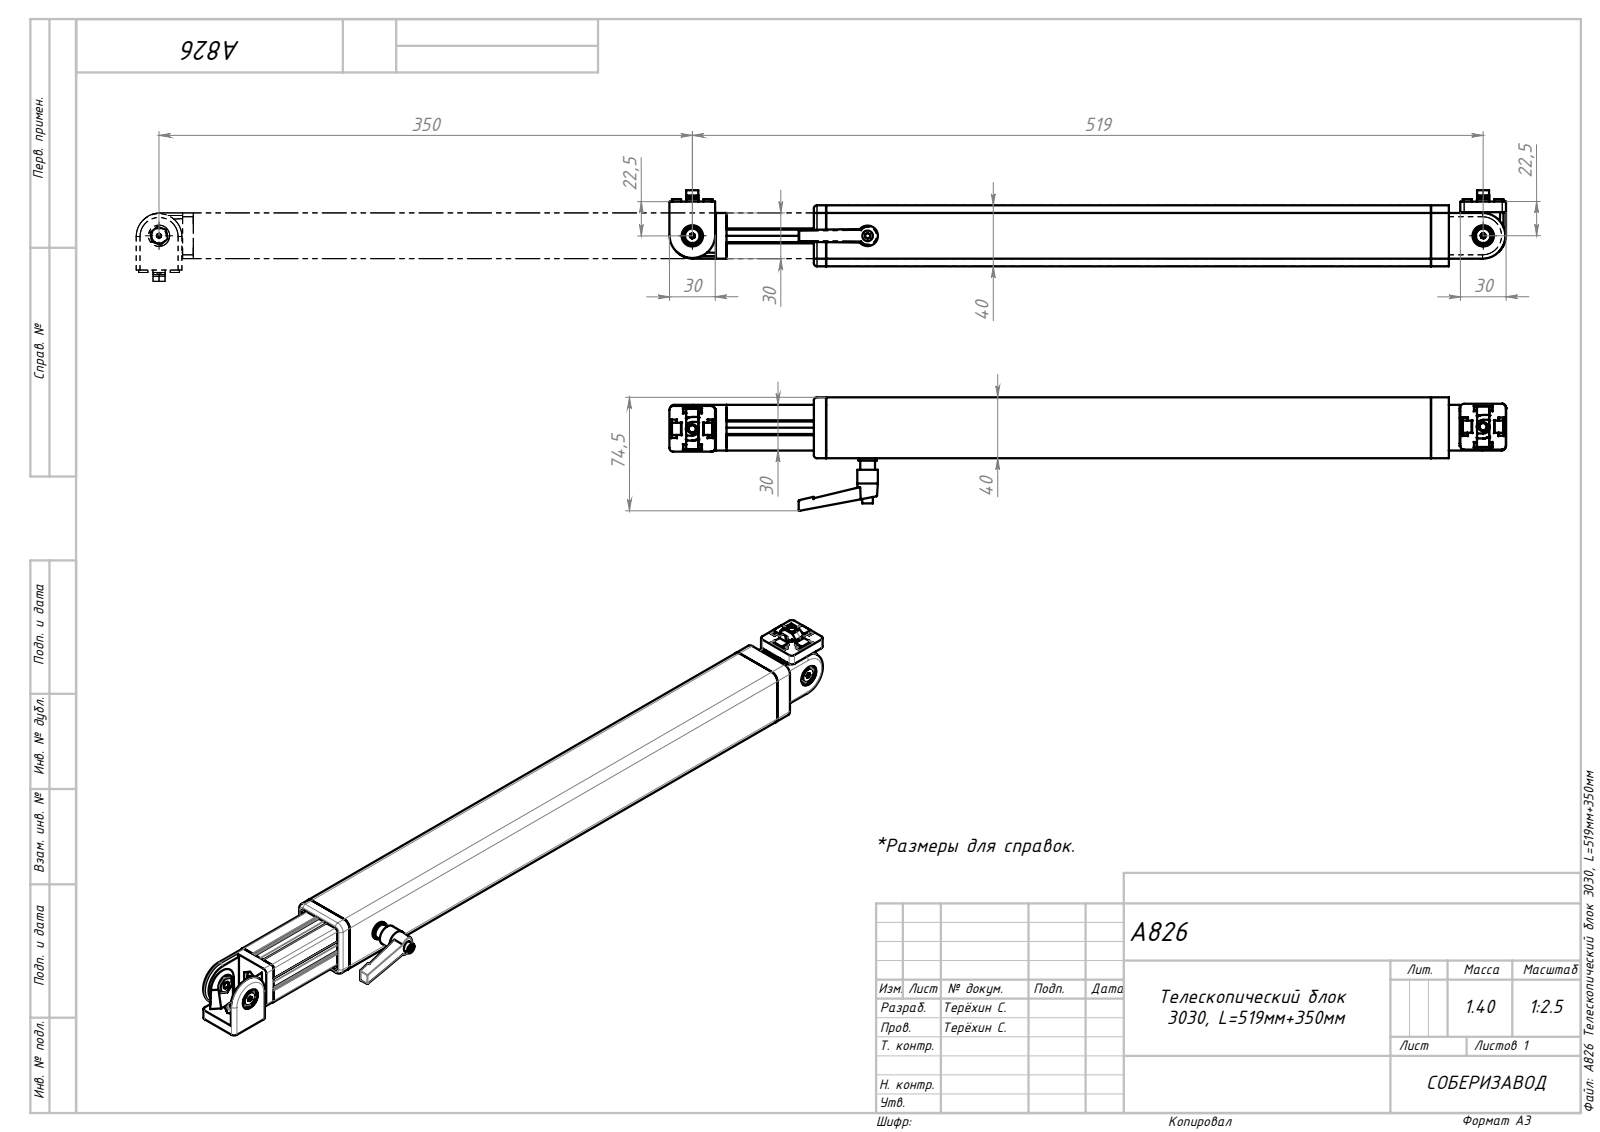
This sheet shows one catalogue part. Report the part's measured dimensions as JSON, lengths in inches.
{"part_name": "Винт M6x10 DIN 912_00; Шарнир 30х30, а_00; Винт с рукояткой М6х12; Шайба 6_00 (+8 more)", "step_written_by": "SolidWorks 2022 (AUTOMOTIVE_DESIGN)", "units": "inches", "bodies": {"solids": 32, "faces": 1271, "planar": 711, "cylindrical": 416, "other": 144}, "overall_size": [21.616, 2.933, 1.964], "volume_in3": 24.63, "surface_area_in2": 466.4, "round_holes": [[0.177, 4], [0.197, 3], [0.327, 3], [0.157, 2], [0.321, 2], [0.551, 2], [0.252, 1], [0.256, 1]], "round_bosses_or_shafts": [[0.236, 4], [0.38, 3], [0.197, 3], [0.394, 2], [0.315, 2], [0.531, 1], [0.472, 1], [0.413, 1]], "partial_cylinders_radius": [[0.012, 91], [0.02, 48], [0.01, 40], [0.03, 24], [0.098, 12], [0.059, 8], [0.079, 8], [0.197, 5]], "face_to_face_distances": [0.138, 1.437, 0.197, 1.378, 0.059, 1.24, 1.575, 1.299, 0.866, 1.063], "hole_center_spacings": [0.64, 0.906, 1.281, 20.433, 4.529, 15.904, 20.432, 20.433]}
